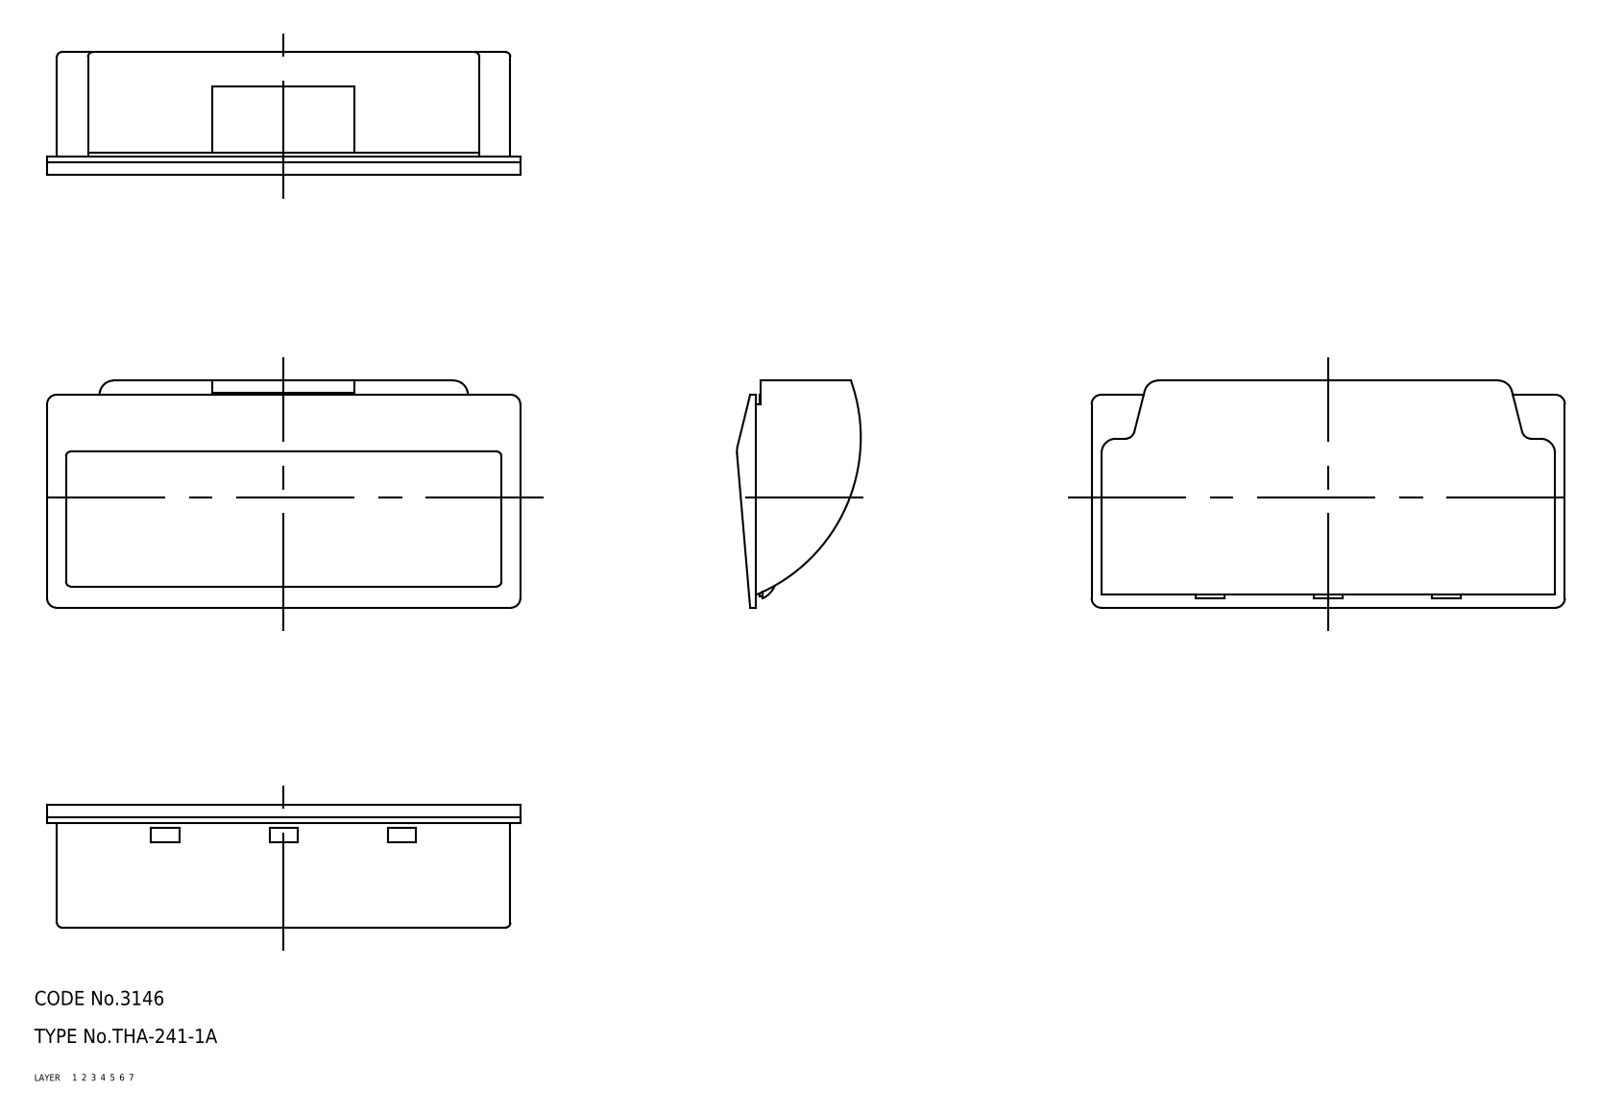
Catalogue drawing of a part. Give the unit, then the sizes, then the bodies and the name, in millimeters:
Units: millimetres
Overall size (bounding box): 100 × 48 × 26
Volume: 24 473 mm³ · Surface area: 19 853 mm²
Bodies: 1 solid, 117 faces (0 planar, 0 cylindrical, 117 other)
Part name (STEP PRODUCT): pull
STEP written by: CADfix (AUTOMOTIVE_DESIGN)
